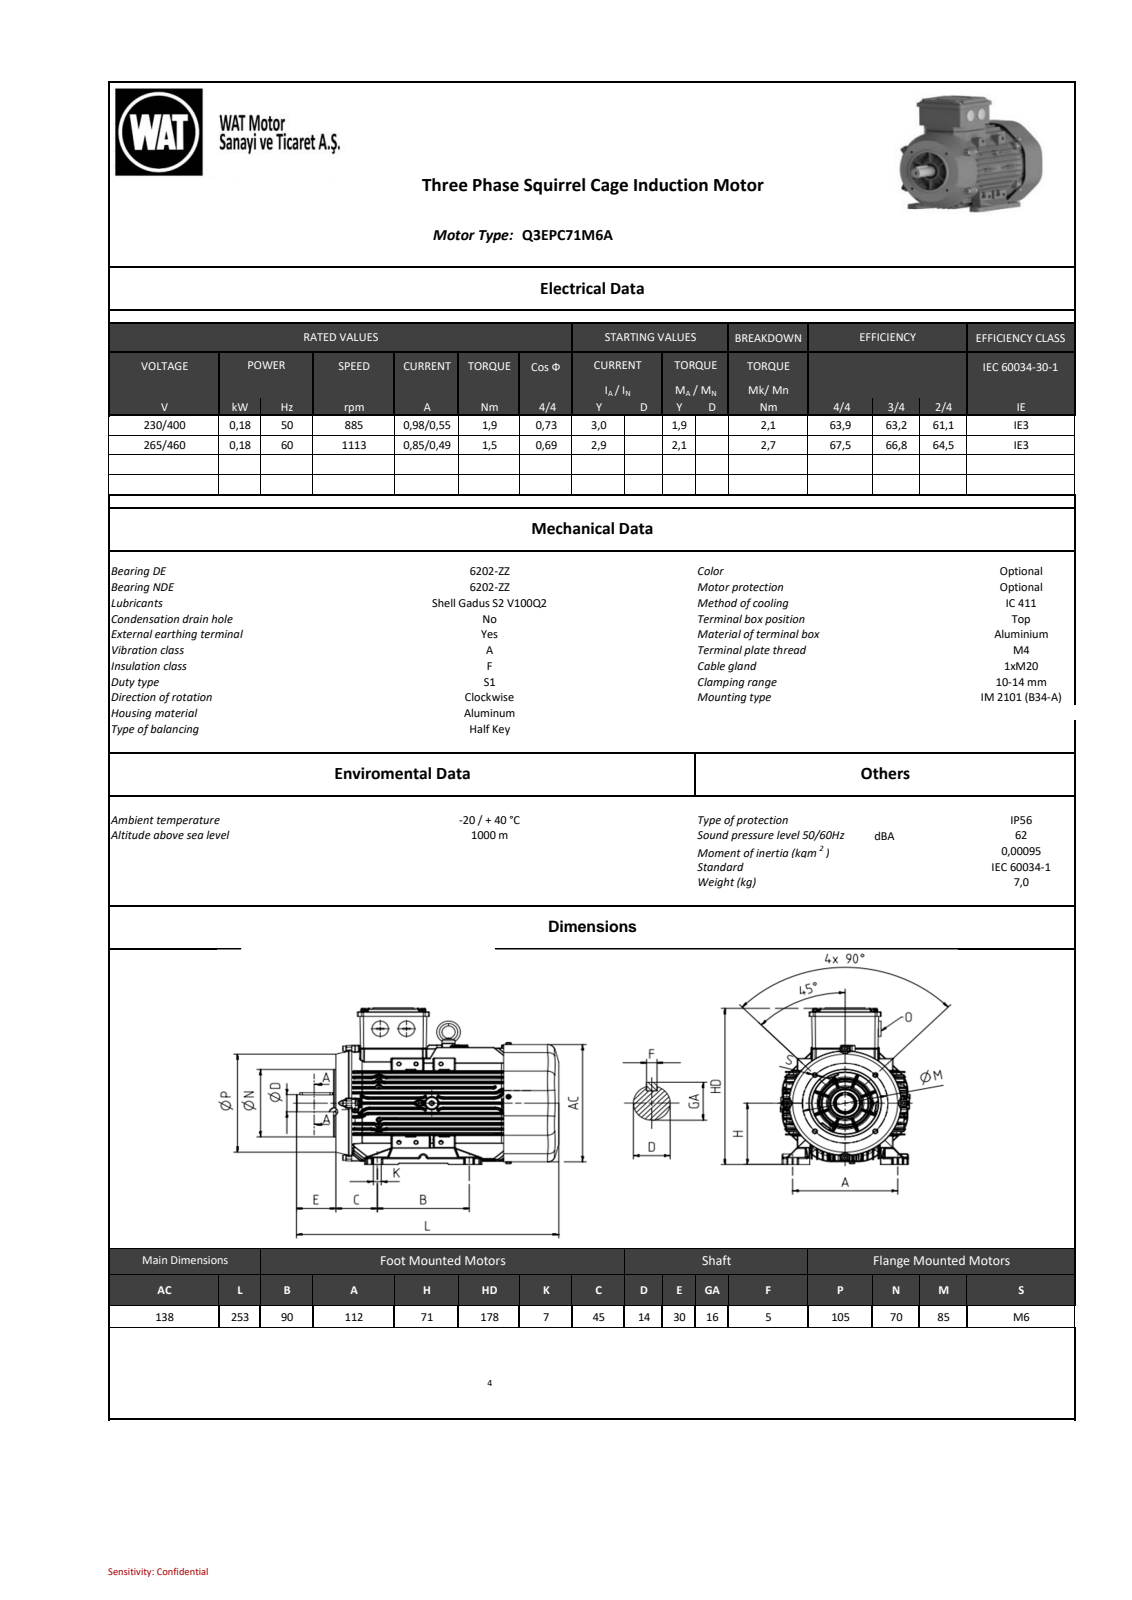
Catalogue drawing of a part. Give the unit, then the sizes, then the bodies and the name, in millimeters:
Units: millimetres
Overall size (bounding box): 252 × 178.11 × 138
Round holes (diameter × count): ⌀3.3 ×9, ⌀3.65 ×8, ⌀3 ×7, ⌀2.5 ×6, ⌀5 ×5, ⌀4.5 ×4, ⌀4.65 ×4, ⌀4.8 ×4, ⌀5.2 ×4, ⌀7 ×4, ⌀3.7 ×3, ⌀4.6 ×2
Round bosses / shafts (diameter × count): ⌀8 ×8, ⌀4 ×8, ⌀12 ×4, ⌀3.3 ×4, ⌀138 ×1, ⌀136 ×1, ⌀70 ×1, ⌀61 ×1
Partial cylindrical surfaces — rounded edges, fillets, slot ends (radius × count): R1 ×127, R0.5 ×57, R1.2 ×36, R1.5 ×28, R2 ×21, R4 ×17, R3.25 ×16, R0.1 ×14
Main face-to-face distances: 2, 3, 1, 4, 5, 15, 35, 83, 182.5, 38
Hole centre spacings: 61.39, 55, 36.59, 67.18, 67.2, 92.35, 60, 8.61
Bodies: 0 solids, 2942 faces (1463 planar, 775 cylindrical, 704 other)
Part name (STEP PRODUCT): 001_objects
STEP written by: SIEMENS PLM Software NX2206.8101 (AUTOMOTIVE_DESIGN)
